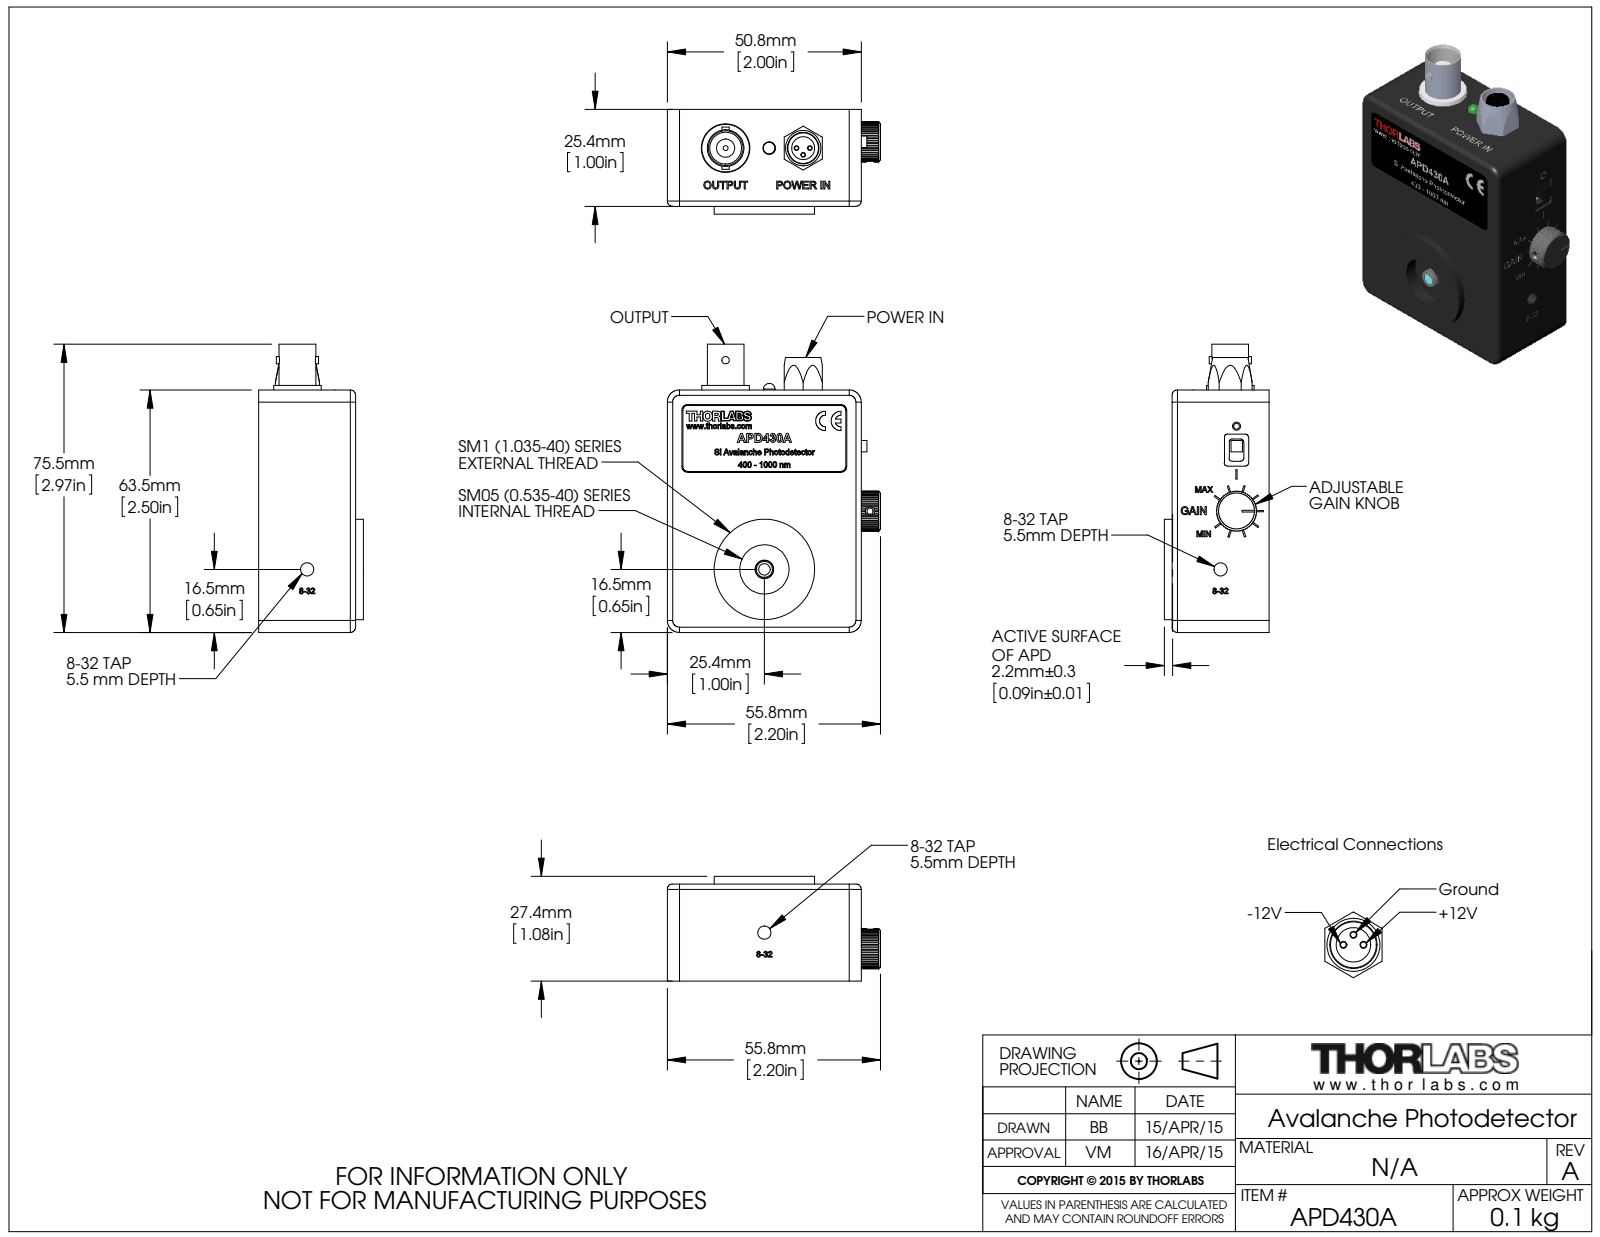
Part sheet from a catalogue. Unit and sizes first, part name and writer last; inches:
Units: inches
Overall size (bounding box): 2.971 × 2.197 × 1.08
Round holes (diameter × count): ⌀0.063 ×9, ⌀0.02 ×6, ⌀0.094 ×4, ⌀0.018 ×2, ⌀0.098 ×2, ⌀0.136 ×2, ⌀0.05 ×1, ⌀0.052 ×1, ⌀0.083 ×1, ⌀0.118 ×1, ⌀0.13 ×1, ⌀0.138 ×1
Round bosses / shafts (diameter × count): ⌀0.039 ×5, ⌀0.15 ×4, ⌀0.079 ×4, ⌀0.065 ×2, ⌀0.063 ×2, ⌀0.051 ×2, ⌀1.035 ×1, ⌀0.49 ×1
Partial cylindrical surfaces — rounded edges, fillets, slot ends (radius × count): R0.012 ×53, R0.125 ×19, R0.13 ×14, R0.031 ×8, R0.095 ×8, R0.02 ×6, R0.075 ×6, R0.008 ×5
Main face-to-face distances: 0.063, 0.1, 0.016, 0.935, 0.872, 1, 0.937, 0.065, 0.984, 0.922
Hole centre spacings: 1.621, 0.174, 2.013, 2.579, 0.098, 1.711, 0.05, 0.079
Bodies: 0 solids, 2374 faces (1208 planar, 436 cylindrical, 730 other)
Part name (STEP PRODUCT): MTN004937
STEP written by: SolidWorks 2014 (AUTOMOTIVE_DESIGN)
